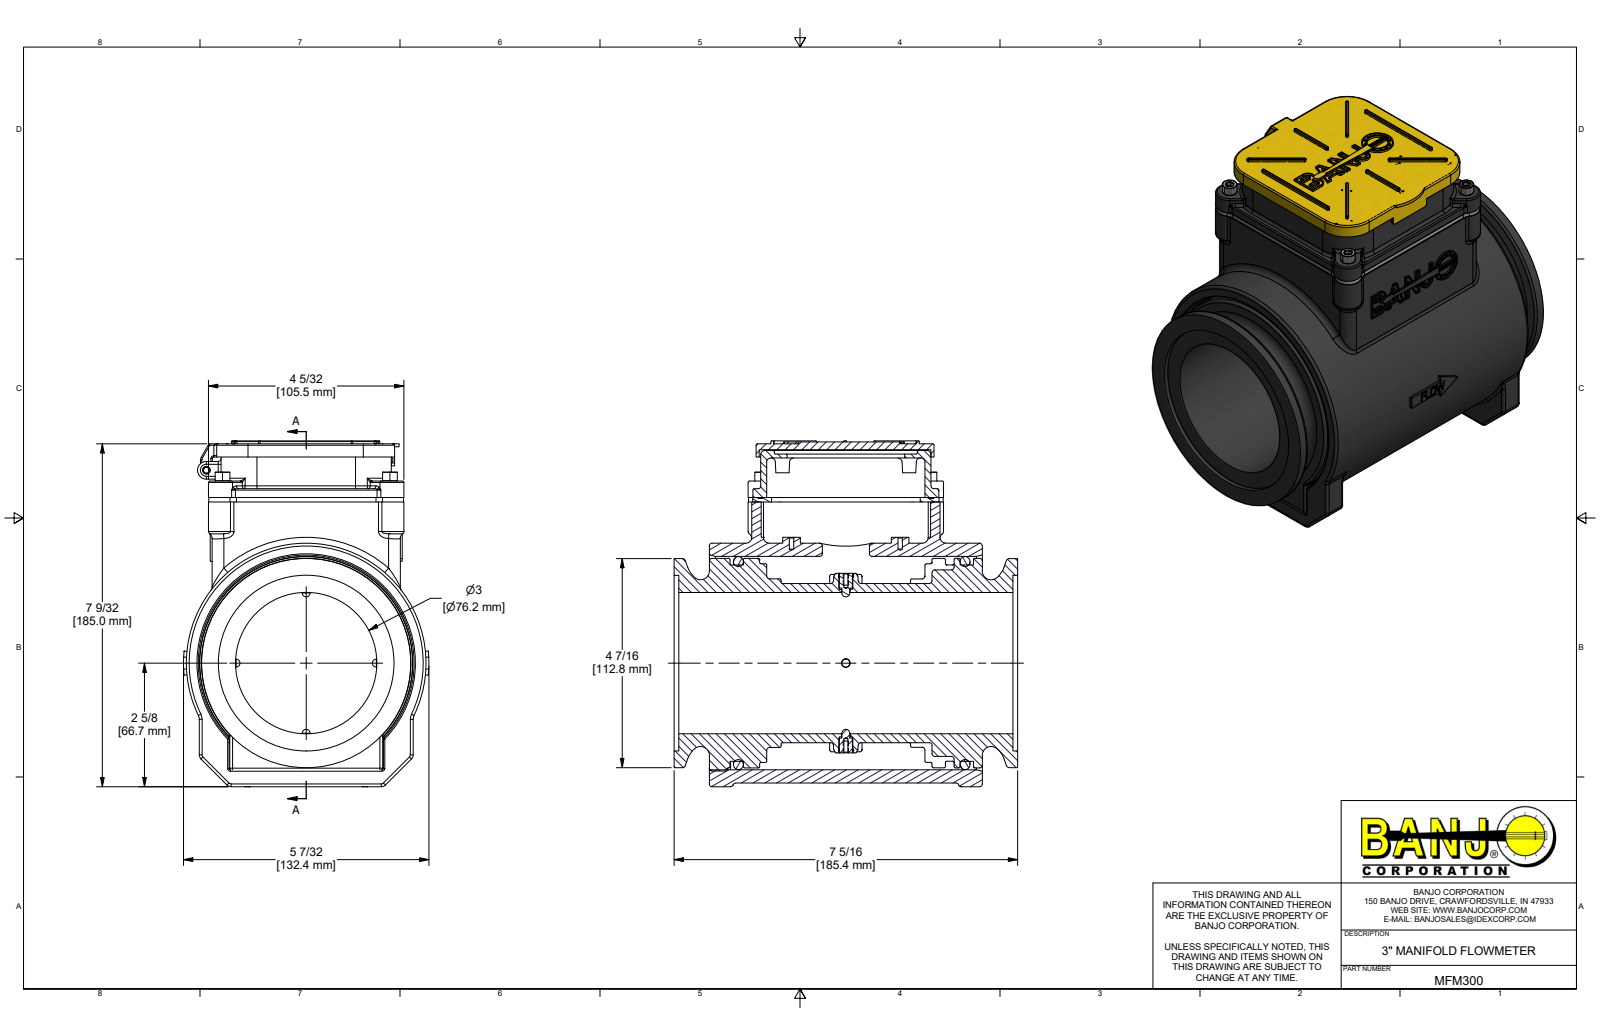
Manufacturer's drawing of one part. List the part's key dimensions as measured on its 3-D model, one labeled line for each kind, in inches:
Part name (STEP PRODUCT): MFM300; M300FML; M300FMLY; M300FMLX (+8 more)
STEP written by: Autodesk Inventor 2019 (AUTOMOTIVE_DESIGN)
Units: inches
Bodies: 17 solids, 14457 faces (10885 planar, 2375 cylindrical, 1197 other)
Overall size (bounding box): 7.345 × 7.3 × 5.214
Volume: 73.34 in³ · Surface area: 585.8 in²
Round holes (diameter × count): ⌀0.114 ×4, ⌀0.156 ×4, ⌀0.2 ×4, ⌀0.219 ×4, ⌀0.33 ×4, ⌀0.454 ×3, ⌀0.641 ×3, ⌀0.085 ×2, ⌀0.094 ×2, ⌀0.104 ×2, ⌀0.15 ×2, ⌀0.184 ×2
Round bosses / shafts (diameter × count): ⌀0.163 ×92, ⌀0.328 ×4, ⌀0.312 ×4, ⌀0.19 ×4, ⌀0.162 ×4, ⌀0.675 ×3, ⌀0.375 ×2, ⌀0.298 ×2
Partial cylindrical surfaces — rounded edges, fillets, slot ends (radius × count): R0.03 ×162, R0.06 ×86, R0.015 ×34, R0.125 ×30, R0.25 ×28, R0.187 ×13, R0.09 ×8, R0.3 ×8
Main face-to-face distances: 0.125, 0.75, 1.11, 1.235, 1.016, 6.55, 0.094, 1.141, 0.65, 4
Hole centre spacings: 3.154, 0.611, 1.36, 1.885, 1.904, 2.515, 2.693, 2.84
